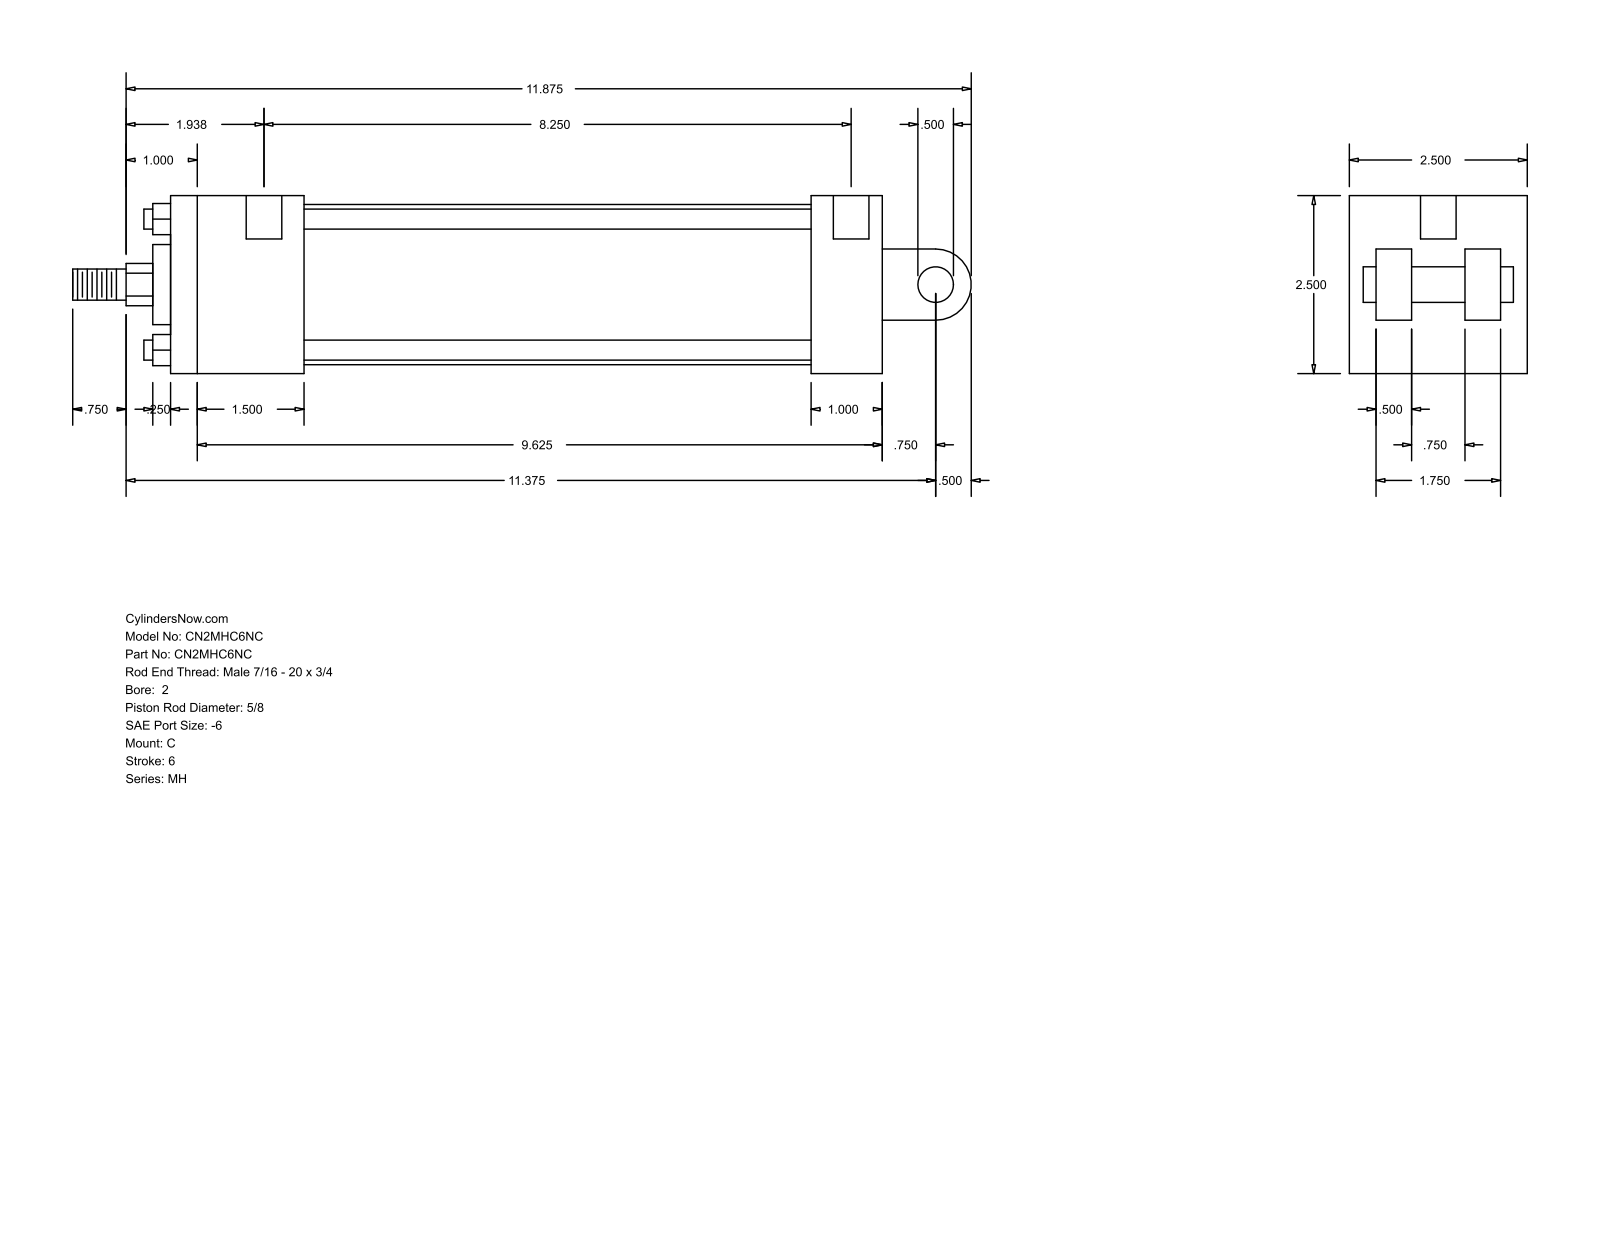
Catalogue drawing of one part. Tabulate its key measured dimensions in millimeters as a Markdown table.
| quantity | value |
| --- | --- |
| part name | MH_C__0200_0.625 |
| STEP written by | GSSL Pune (CONFIG_CONTROL_DESIGN) |
| units | millimeters |
| bodies | 0 solids, 99 faces (70 planar, 29 cylindrical, 0 other) |
| overall size | 320.68 × 63.5 × 63.5 |
| round holes (diameter × count) | 5.56 × 4, 12.7 × 2 |
| round bosses / shafts (diameter × count) | 7.14 × 4, 57.15 × 1, 28.57 × 1, 15.88 × 1, 12.7 × 1, 11.11 × 1 |
| partial cylindrical surfaces (radius × count) | 7.54 × 1, 12.7 × 1 |
| main face-to-face distances | 63.5, 254, 12.7, 47.62, 228.59, 180.97, 206.38, 25.41, 19.05, 22.22 |
| hole center spacings | 217.49, 3.18, 4.76, 209.55, 212.73, 214.31 |
